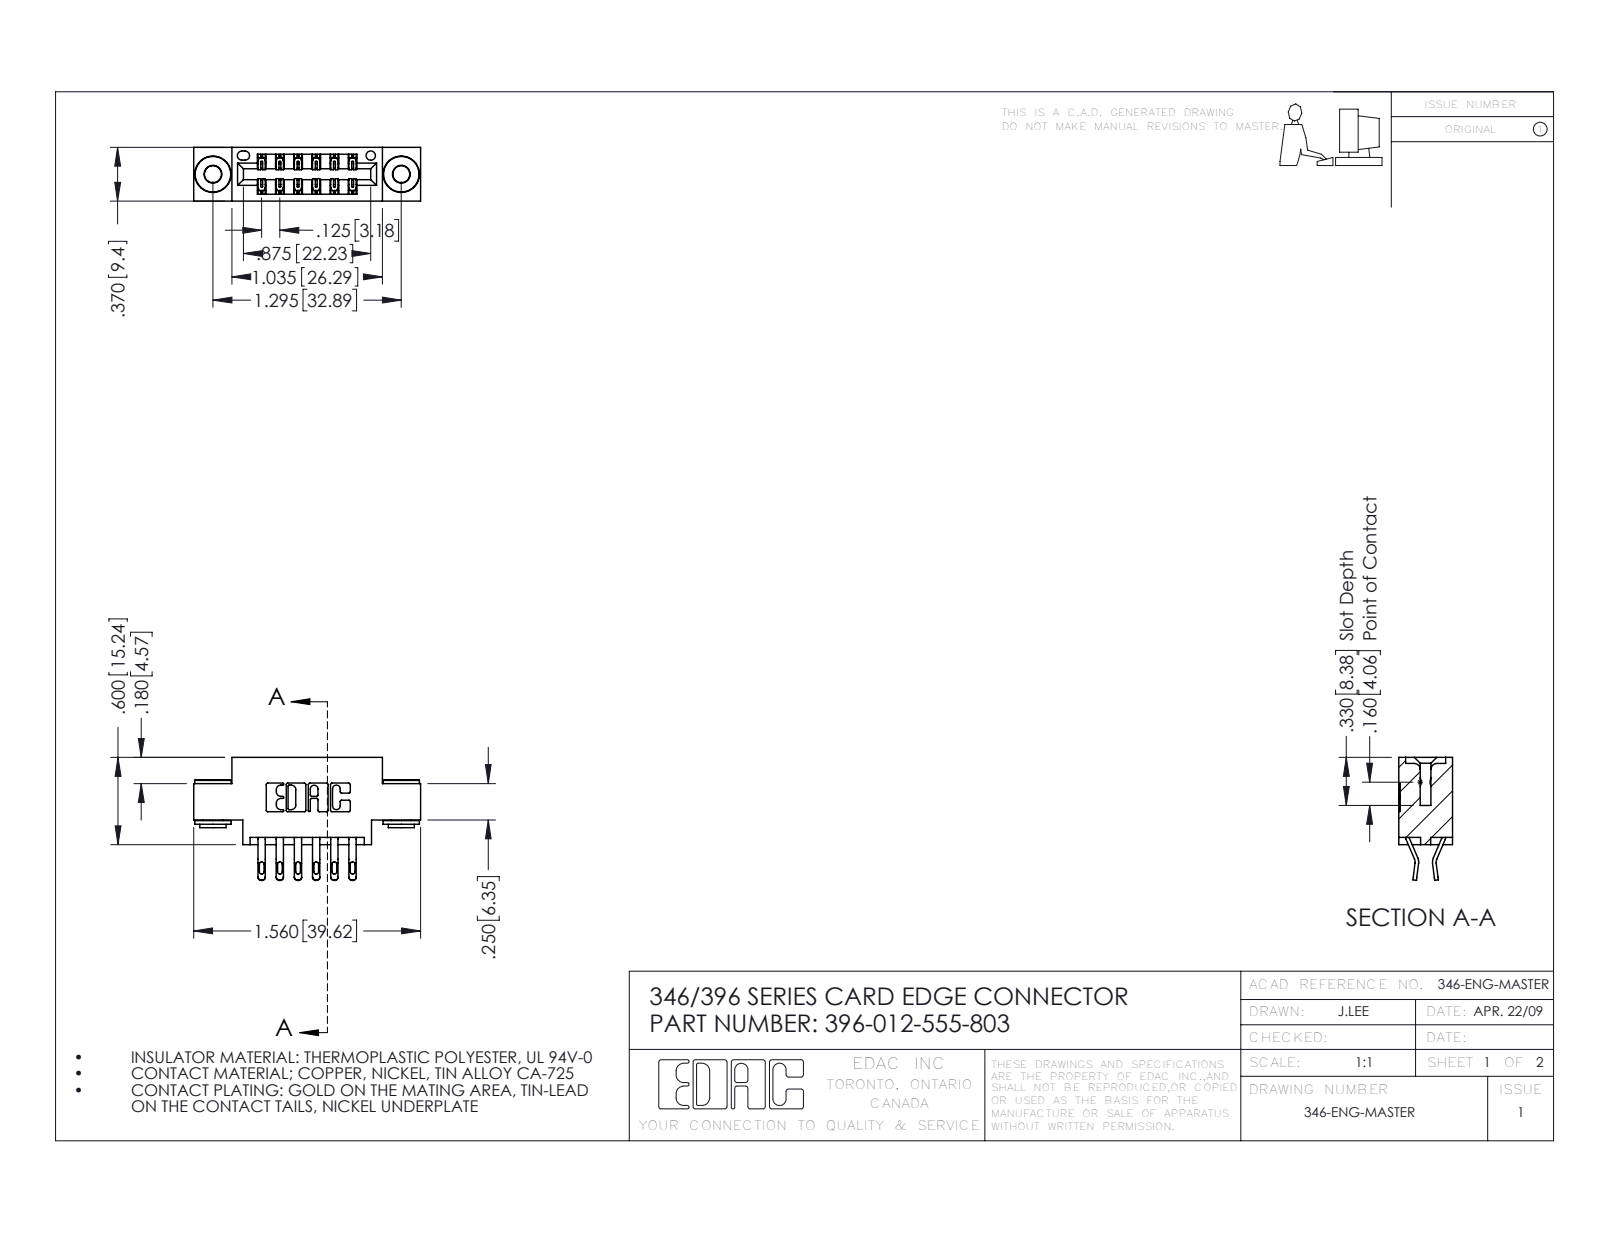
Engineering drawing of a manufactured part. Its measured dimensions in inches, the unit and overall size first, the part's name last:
Units: inches
Overall size (bounding box): 1.56 × 0.845 × 0.37
Round holes (diameter × count): ⌀0.116 ×2, ⌀0.156 ×2, ⌀0.064 ×1
Round bosses / shafts (diameter × count): ⌀0.25 ×2, ⌀0.18 ×2, ⌀0.136 ×2
Partial cylindrical surfaces — rounded edges, fillets, slot ends (radius × count): R0.016 ×24, R0.02 ×24, R0.01 ×22, R0.006 ×18, R0.007 ×6, R0.031 ×6, R0.026 ×3, R0.01 ×2
Main face-to-face distances: 0.25, 0.37, 0.048, 0.322, 0.025, 0.275, 0.148, 0.222, 0.1, 0.174
Hole centre spacings: 0.246, 1.092, 1.295
Volume: 0.213 in³ · Surface area: 7.348 in²
Bodies: 15 solids, 860 faces (486 planar, 366 cylindrical, 8 other)
Part name (STEP PRODUCT): 345-250-002_345-250-002-102; 345-292-001_555 Tail; 396-012-555-803; 346 Part_0.170 Offset - 0.156 Dia-TH
STEP written by: SolidWorks 2016 (CONFIG_CONTROL_DESIGN)
